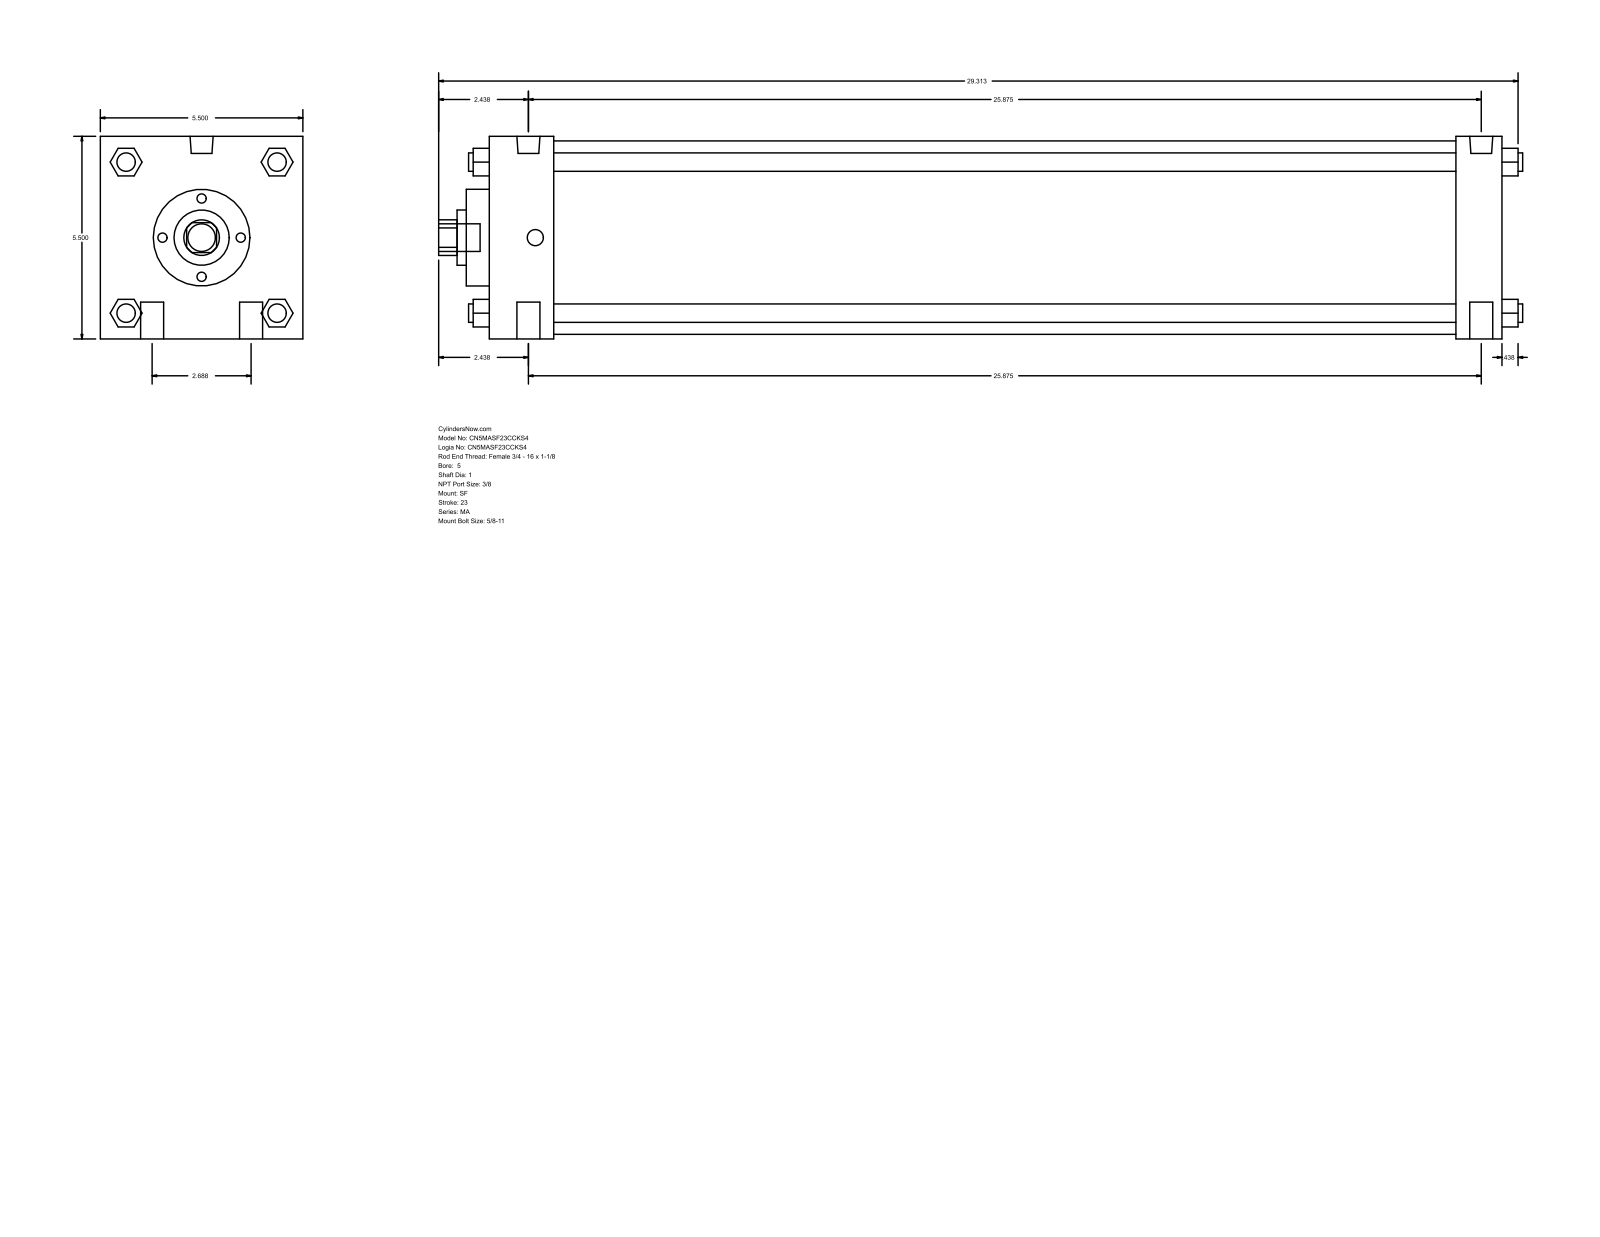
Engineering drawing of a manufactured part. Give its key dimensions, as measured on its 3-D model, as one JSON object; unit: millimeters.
{"part_name": "MA_SF__0500_1", "step_written_by": "GSSL Pune (CONFIG_CONTROL_DESIGN)", "units": "millimeters", "bodies": {"solids": 0, "faces": 126, "planar": 95, "cylindrical": 31, "other": 0}, "overall_size": [747.71, 139.7, 139.7], "round_holes": [[25.4, 1], [38.1, 1], [66.67, 1], [133.35, 1]], "round_bosses_or_shafts": [[15.88, 4], [12.7, 4], [15.93, 2], [11.11, 2], [19.05, 1]], "partial_cylinders_radius": [[12.29, 1]], "face_to_face_distances": [139.7, 698.5, 44.46, 666.75, 622.29, 654.04, 31.75, 15.87, 60.33, 682.62]}
